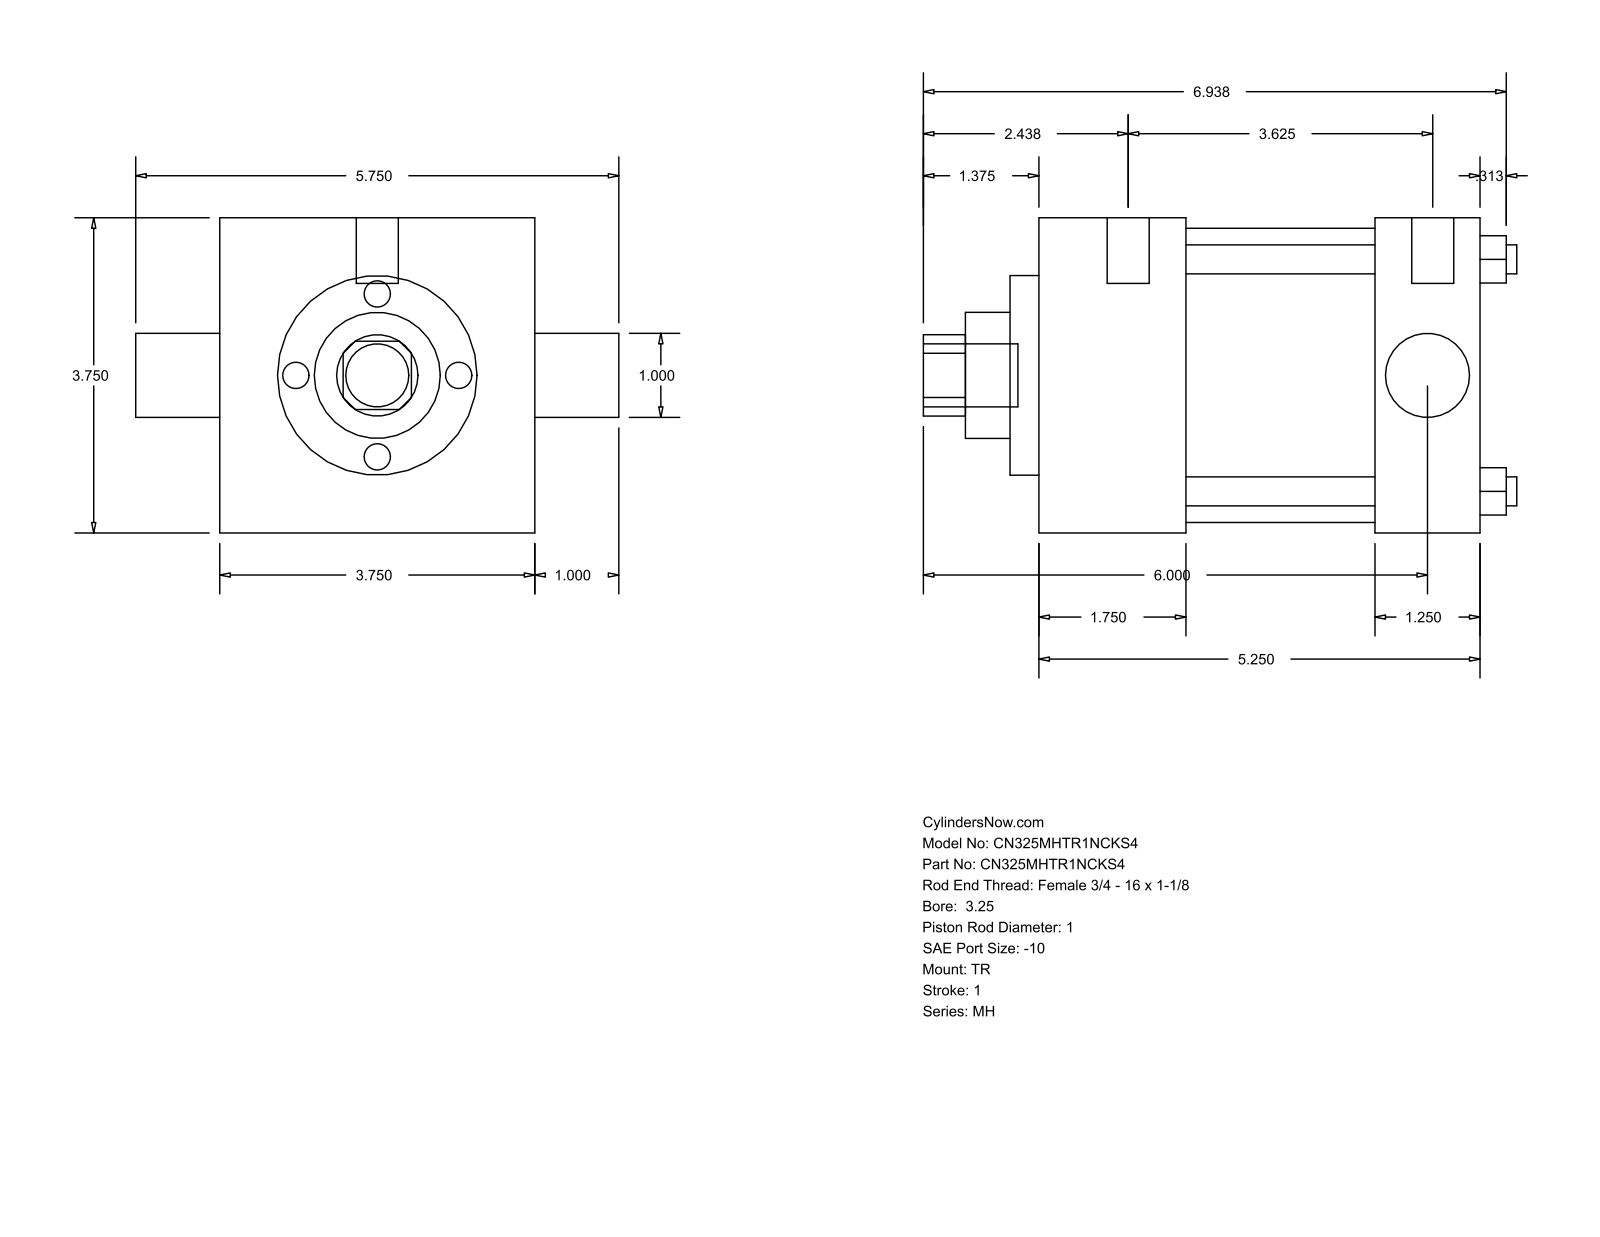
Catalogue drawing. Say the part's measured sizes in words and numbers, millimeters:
The part is named "MH_TR__0325_1". Its 3-D file was written by "GSSL Pune (CONFIG_CONTROL_DESIGN)". It is 0 solids with 86 faces: 61 planar, 25 cylindrical and 0 other. Overall it measures 179.39 by 146.05 by 95.25 millimeters. Round holes: 4 of diameter 8.76, 2 of diameter 25.4, 1 of diameter 38.1, 1 of diameter 60.33, 1 of diameter 88.9. Round bosses or shafts: 3 of diameter 5.56, 2 of diameter 12.7, 1 of diameter 19.05. Partial cylindrical surfaces (rounded edges, fillets, slot ends): 1 of radius 12.29. The main face-to-face distances are 95.24, 133.36, 44.46, 101.61, 57.15, 88.9, 31.75, 8.73, 53.19, 110.34. The hole center spacings are 49.57, 70.1, 99.14.
